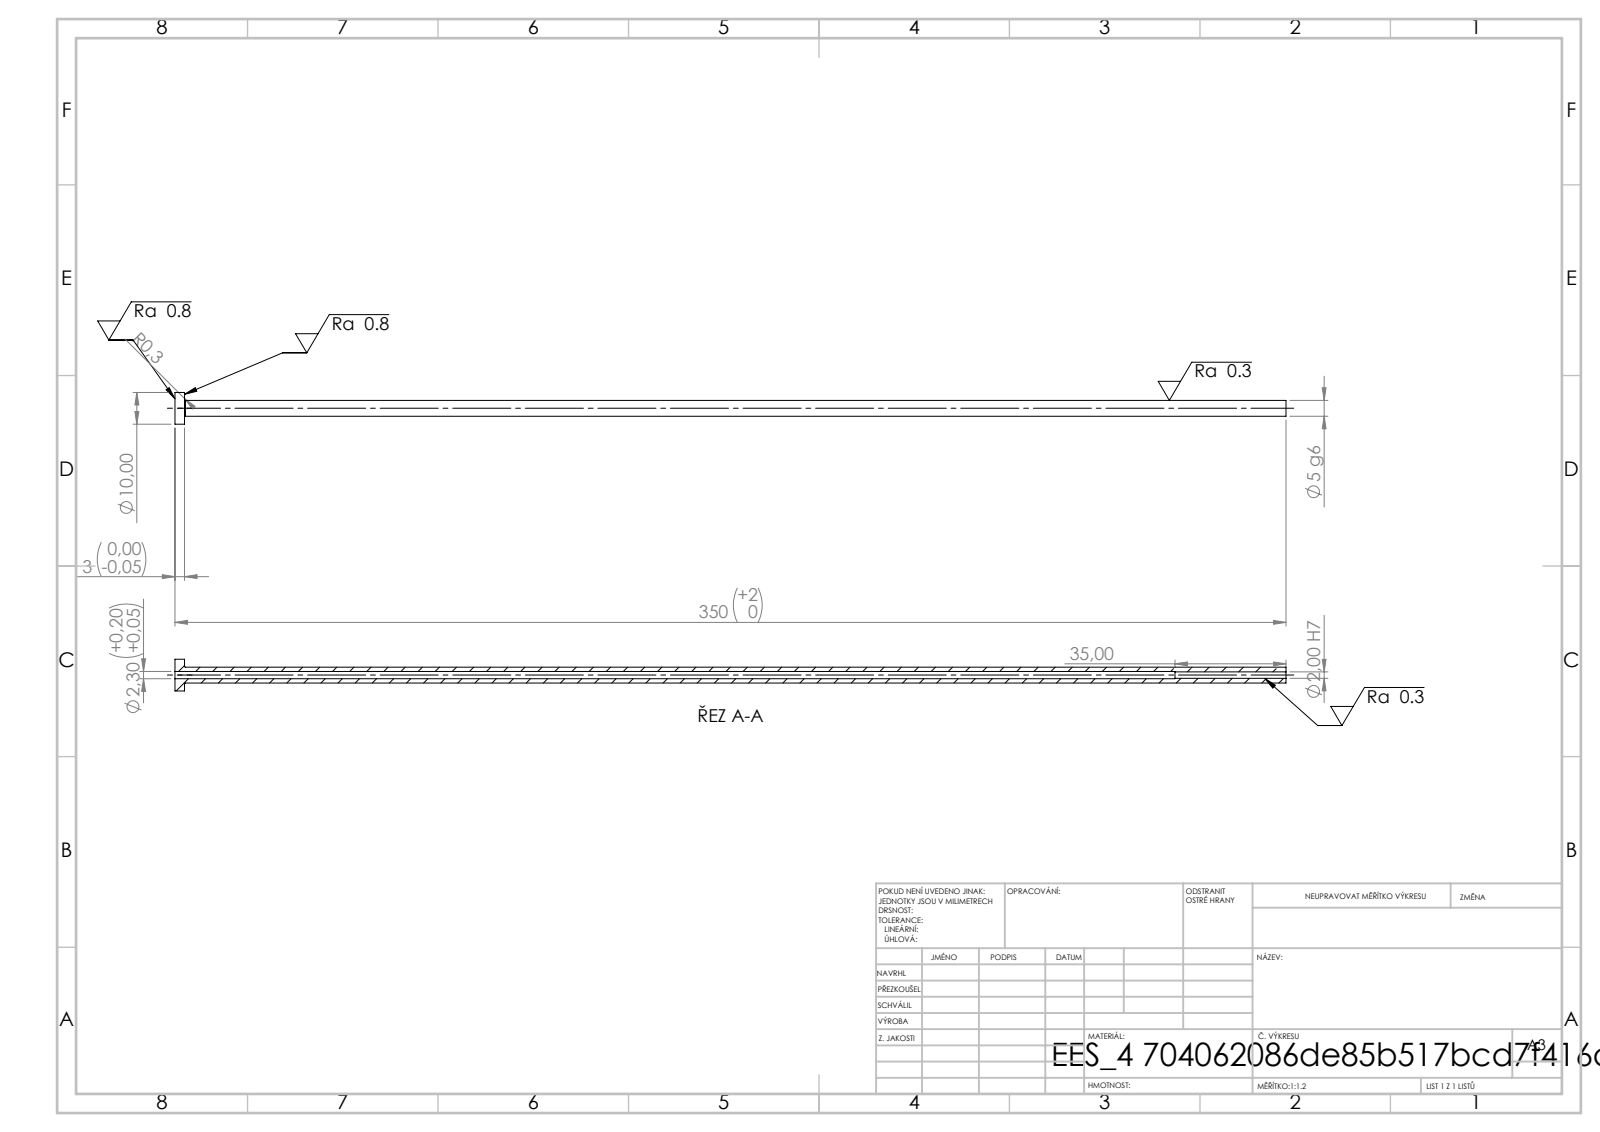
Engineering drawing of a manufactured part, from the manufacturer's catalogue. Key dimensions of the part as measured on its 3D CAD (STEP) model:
STEP written by: SolidWorks 2019 (CONFIG_CONTROL_DESIGN)
Units: millimetres
Bodies: 1 solid, 14 faces (4 planar, 8 cylindrical, 2 other)
Overall size (bounding box): 350 × 10 × 10
Volume: 5 631 mm³ · Surface area: 8 190 mm²
Round holes (diameter × count): ⌀2 ×1, ⌀2.3 ×1
Round bosses / shafts (diameter × count): ⌀10 ×1, ⌀5 ×1
Main face-to-face distances: 3, 350, 347, 315, 312, 35
